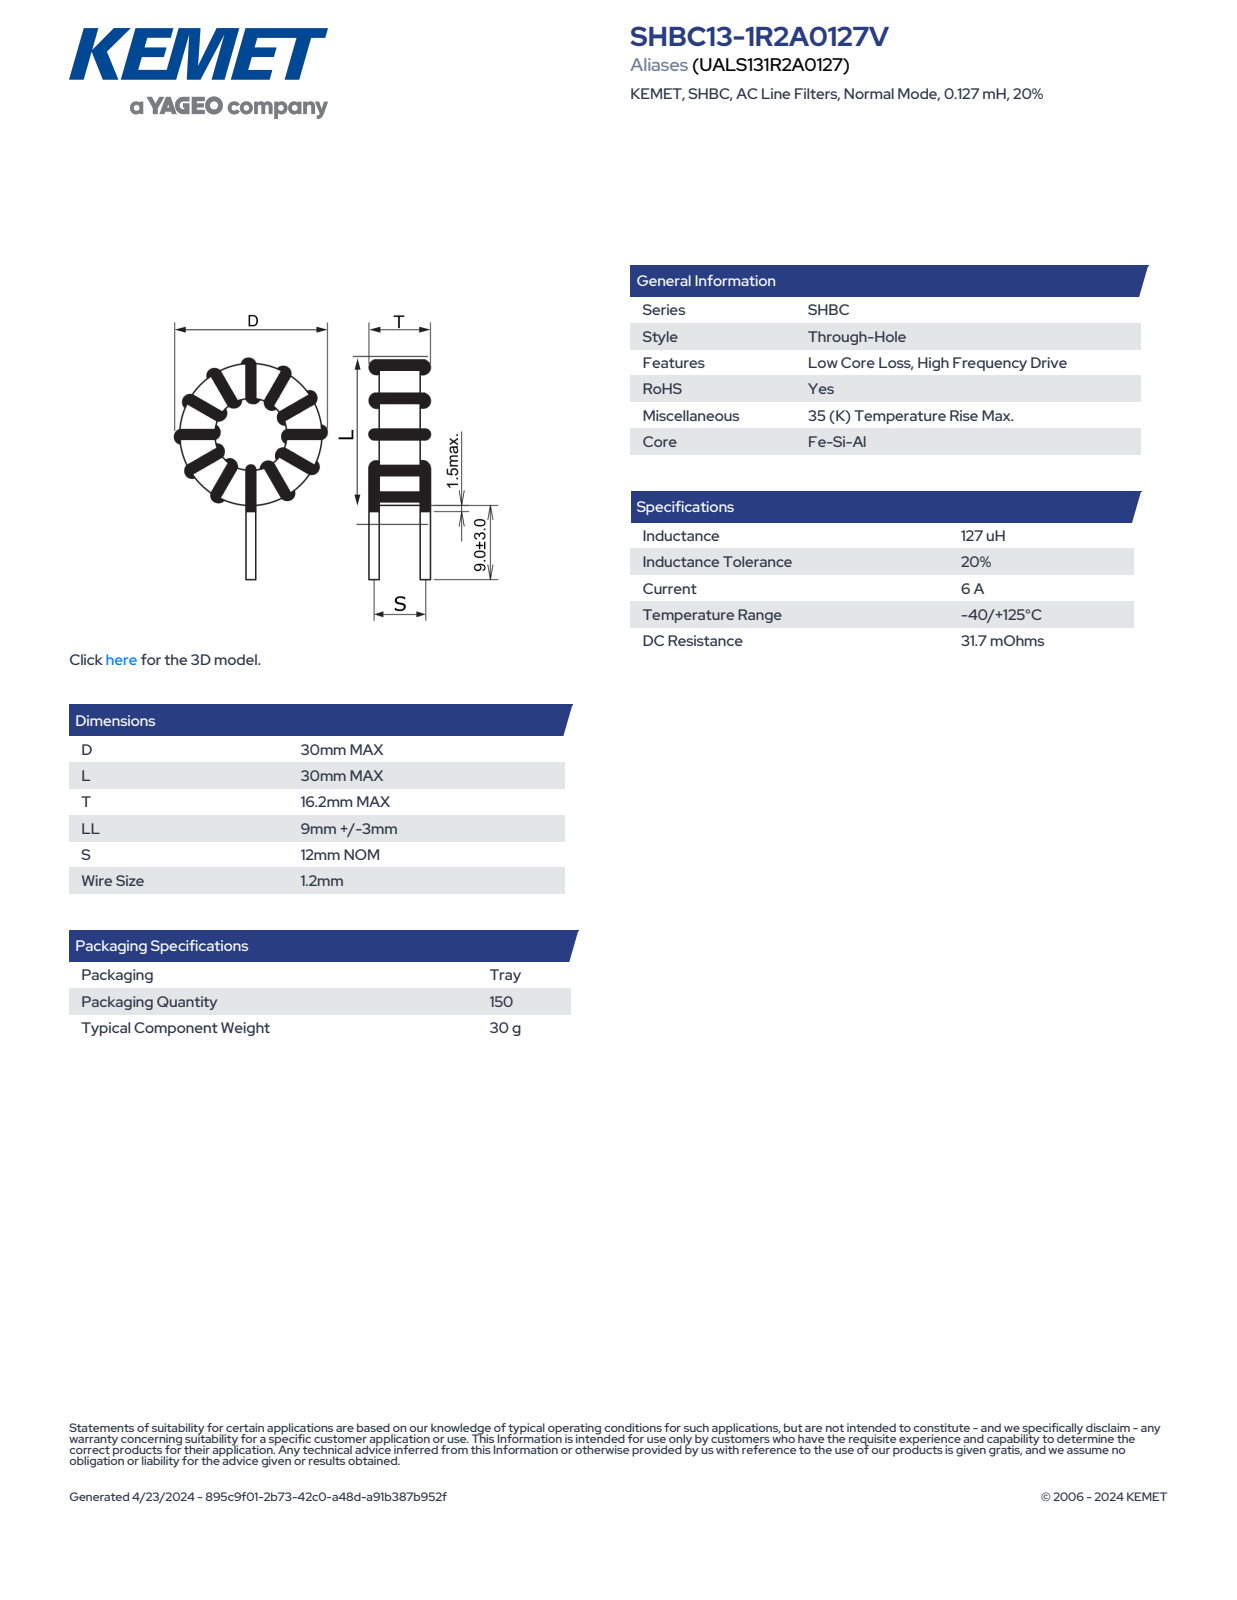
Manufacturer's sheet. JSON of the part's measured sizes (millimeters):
{"part_name": "SHBC13-1R2A0127V", "step_written_by": "SolidWorks 2018 (AUTOMOTIVE_DESIGN)", "units": "millimeters", "bodies": {"solids": 1, "faces": 78, "planar": 14, "cylindrical": 42, "other": 22}, "overall_size": [39, 30, 16.2], "volume_mm3": 9630, "surface_area_mm2": 3524, "round_holes": [[11.37, 1]], "round_bosses_or_shafts": [[1.2, 3], [30, 1]], "partial_cylinders_radius": [[0.6, 8], [6.88, 1], [12.15, 1], [15, 1]], "face_to_face_distances": [16.2, 3.25, 12.95, 6.6, 9.6, 3.35, 6.35, 9.7, 3]}
